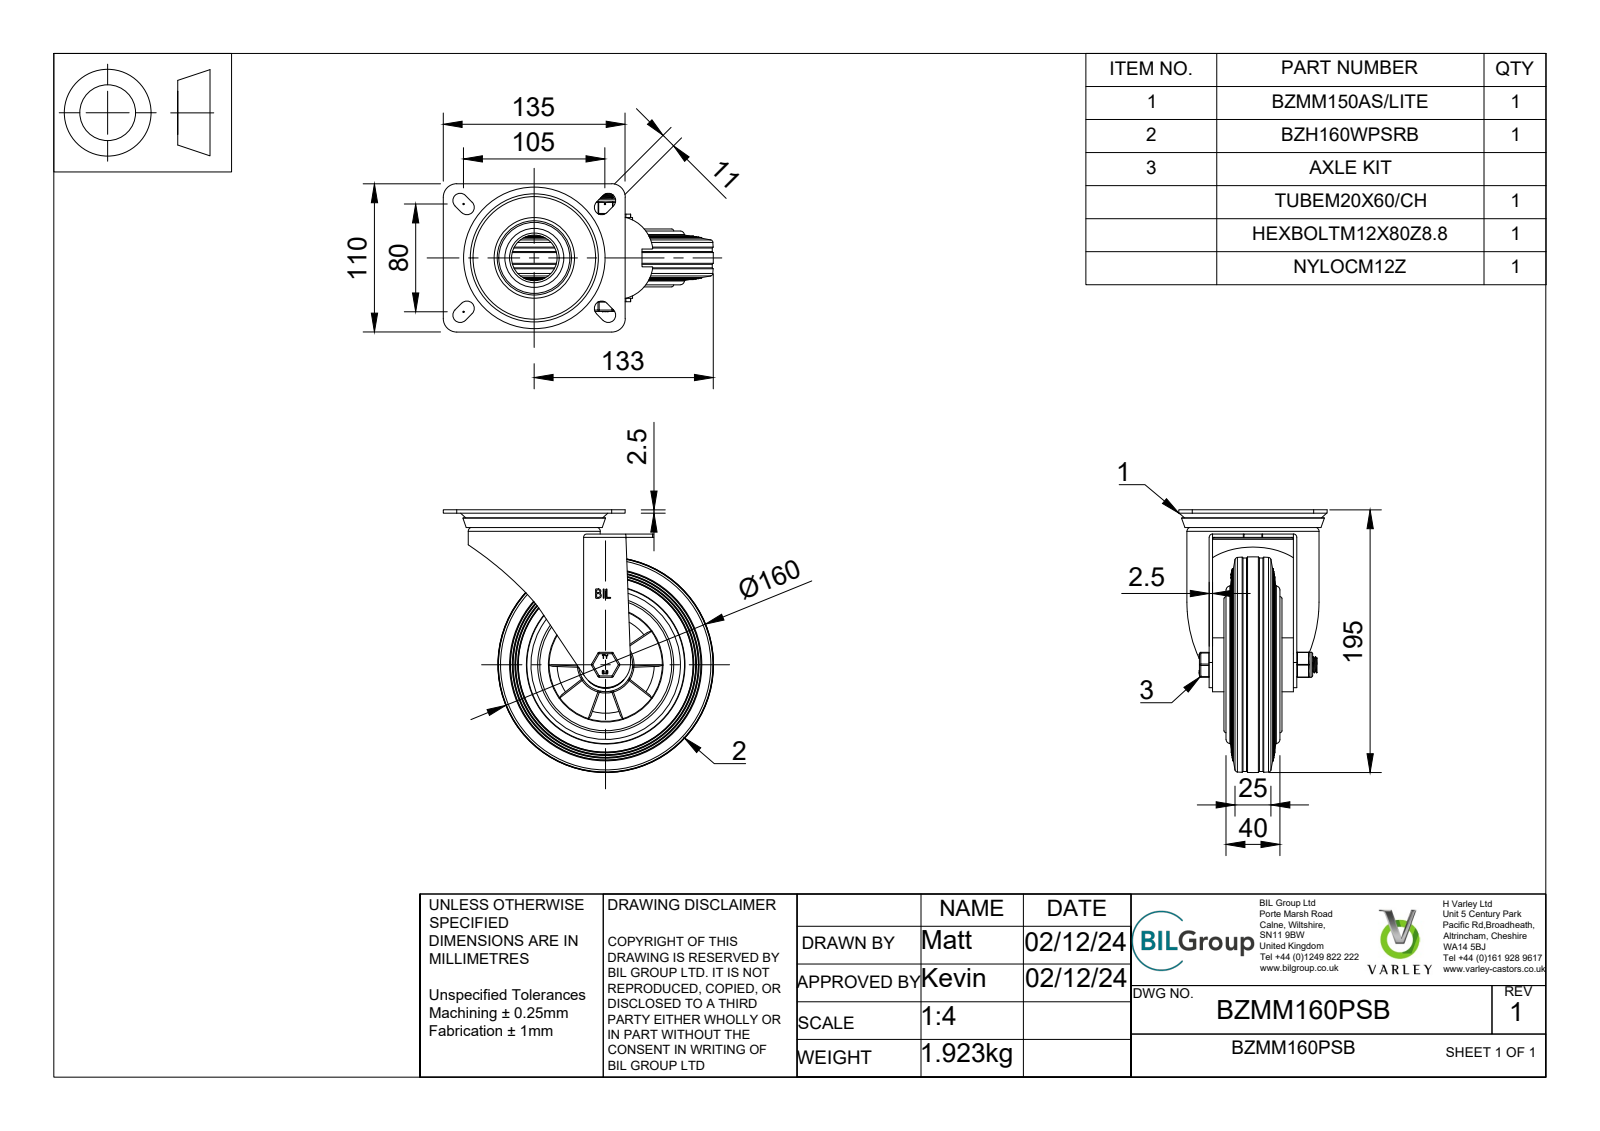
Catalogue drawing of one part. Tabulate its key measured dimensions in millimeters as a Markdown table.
| quantity | value |
| --- | --- |
| part name | BZMM160PSB v4; BZMM150AS/LITE - 2 v3; ZINC PLATED, PRESSED STEEL TOP PLATE; ZINC PLATED, PRESSED STEEL TOP PLATE Geometry (+7 more) |
| STEP written by | Autodesk Translation Framework v13.20.0.188 (AP242_MANAGED_MODEL_BASED_3D_ENGINEERING_MIM_LF) |
| units | millimeters |
| bodies | 59 solids, 758 faces (222 planar, 169 cylindrical, 367 other) |
| overall size | 200.5 × 195 × 110 |
| volume | 754 365 mm³ |
| surface area | 256 173 mm² |
| round holes (diameter × count) | 12 × 1, 12.2 × 1, 12.5 × 1, 14 × 1, 20 × 1, 33.75 × 1, 34 × 1, 35 × 1, 39.75 × 1, 72 × 1, 85 × 1, 93 × 1 |
| round bosses / shafts (diameter × count) | 7.5 × 8, 158.4 × 1, 101 × 1, 98 × 1, 78 × 1, 50 × 1, 40 × 1, 34.9 × 1 |
| partial cylindrical surfaces (radius × count) | 0.5 × 20, 1 × 12, 5.5 × 8, 1.5 × 4, 10 × 4, 2.5 × 2, 26.89 × 2, 13.5 × 1 |
| main face-to-face distances | 2.5, 9, 5, 18, 62.5, 3, 60, 4, 2, 16 |
